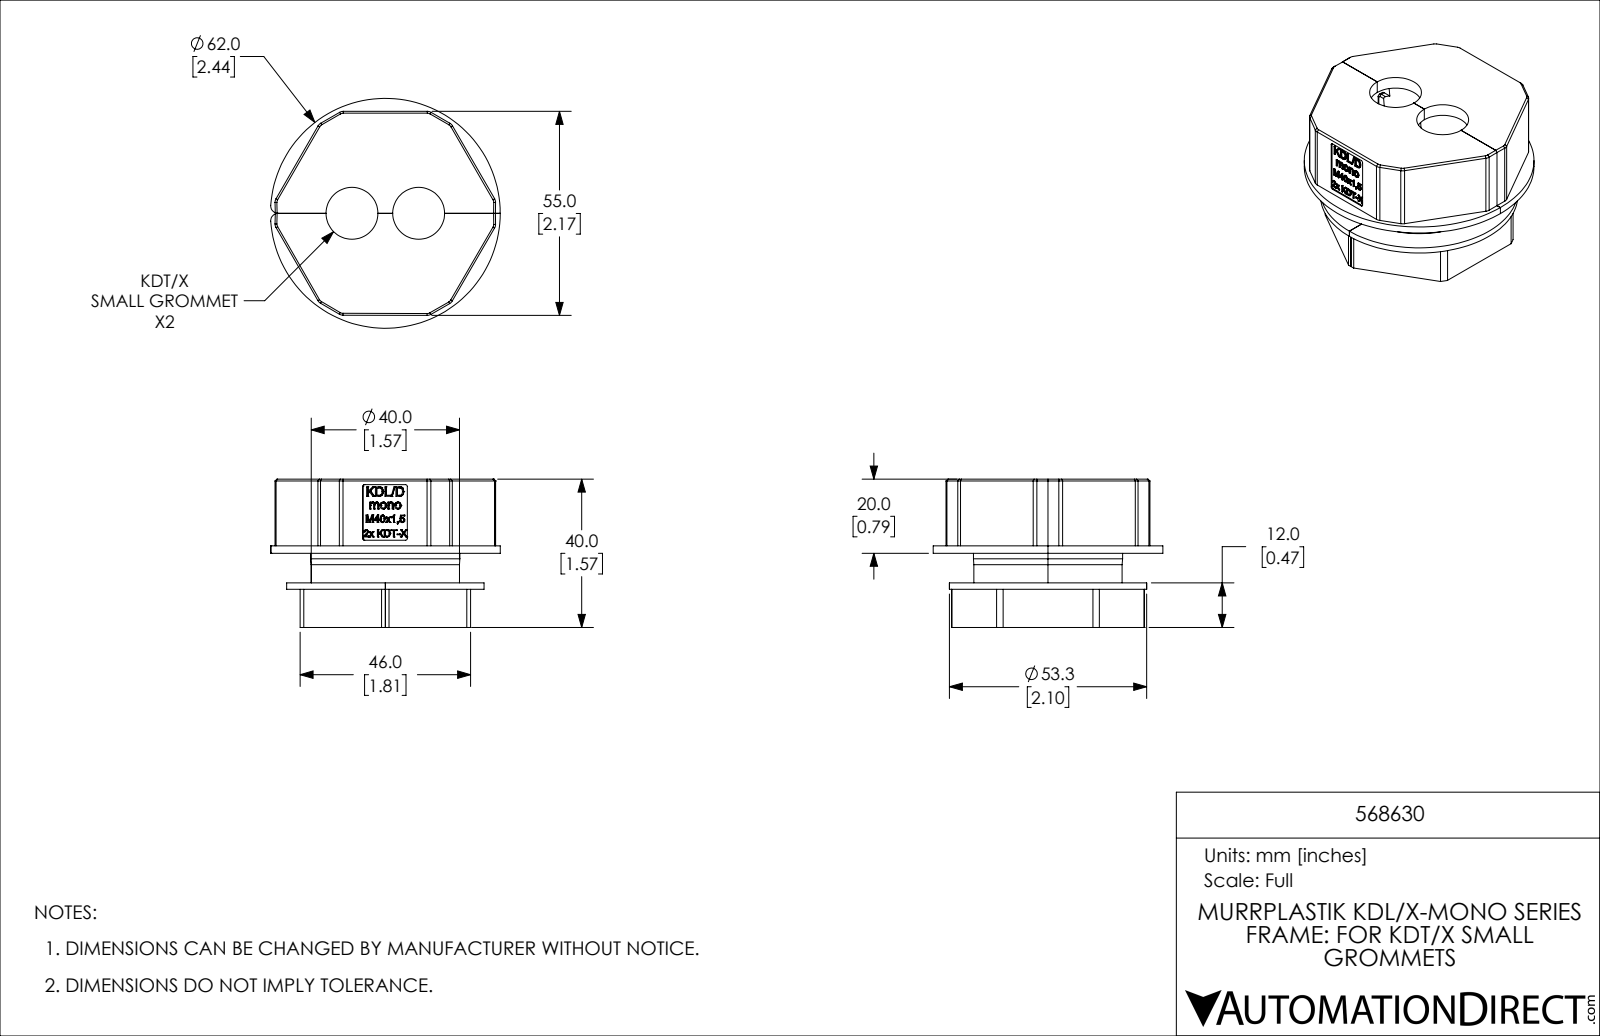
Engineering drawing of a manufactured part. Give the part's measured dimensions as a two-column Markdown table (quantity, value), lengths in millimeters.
| quantity | value |
| --- | --- |
| part name | 568630 |
| STEP written by | SolidWorks 2019 (CONFIG_CONTROL_DESIGN) |
| units | millimeters |
| bodies | 2 solids, 606 faces (339 planar, 100 cylindrical, 167 other) |
| overall size | 62 × 61.93 × 40 |
| volume | 51 796 mm³ |
| surface area | 17 530 mm² |
| round holes (diameter × count) | 14 × 2, 15.14 × 2, 33.2 × 1 |
| round bosses / shafts (diameter × count) | 62 × 1, 40.25 × 1, 40 × 1 |
| partial cylindrical surfaces (radius × count) | 0.5 × 14, 2 × 14, 0.32 × 4, 0.4 × 4, 0.64 × 4, 1 × 2 |
| main face-to-face distances | 20, 21.45, 1.45, 2, 18, 3.45, 4.65, 16.5, 3.5, 40 |
| hole center spacings | 9, 18 |
